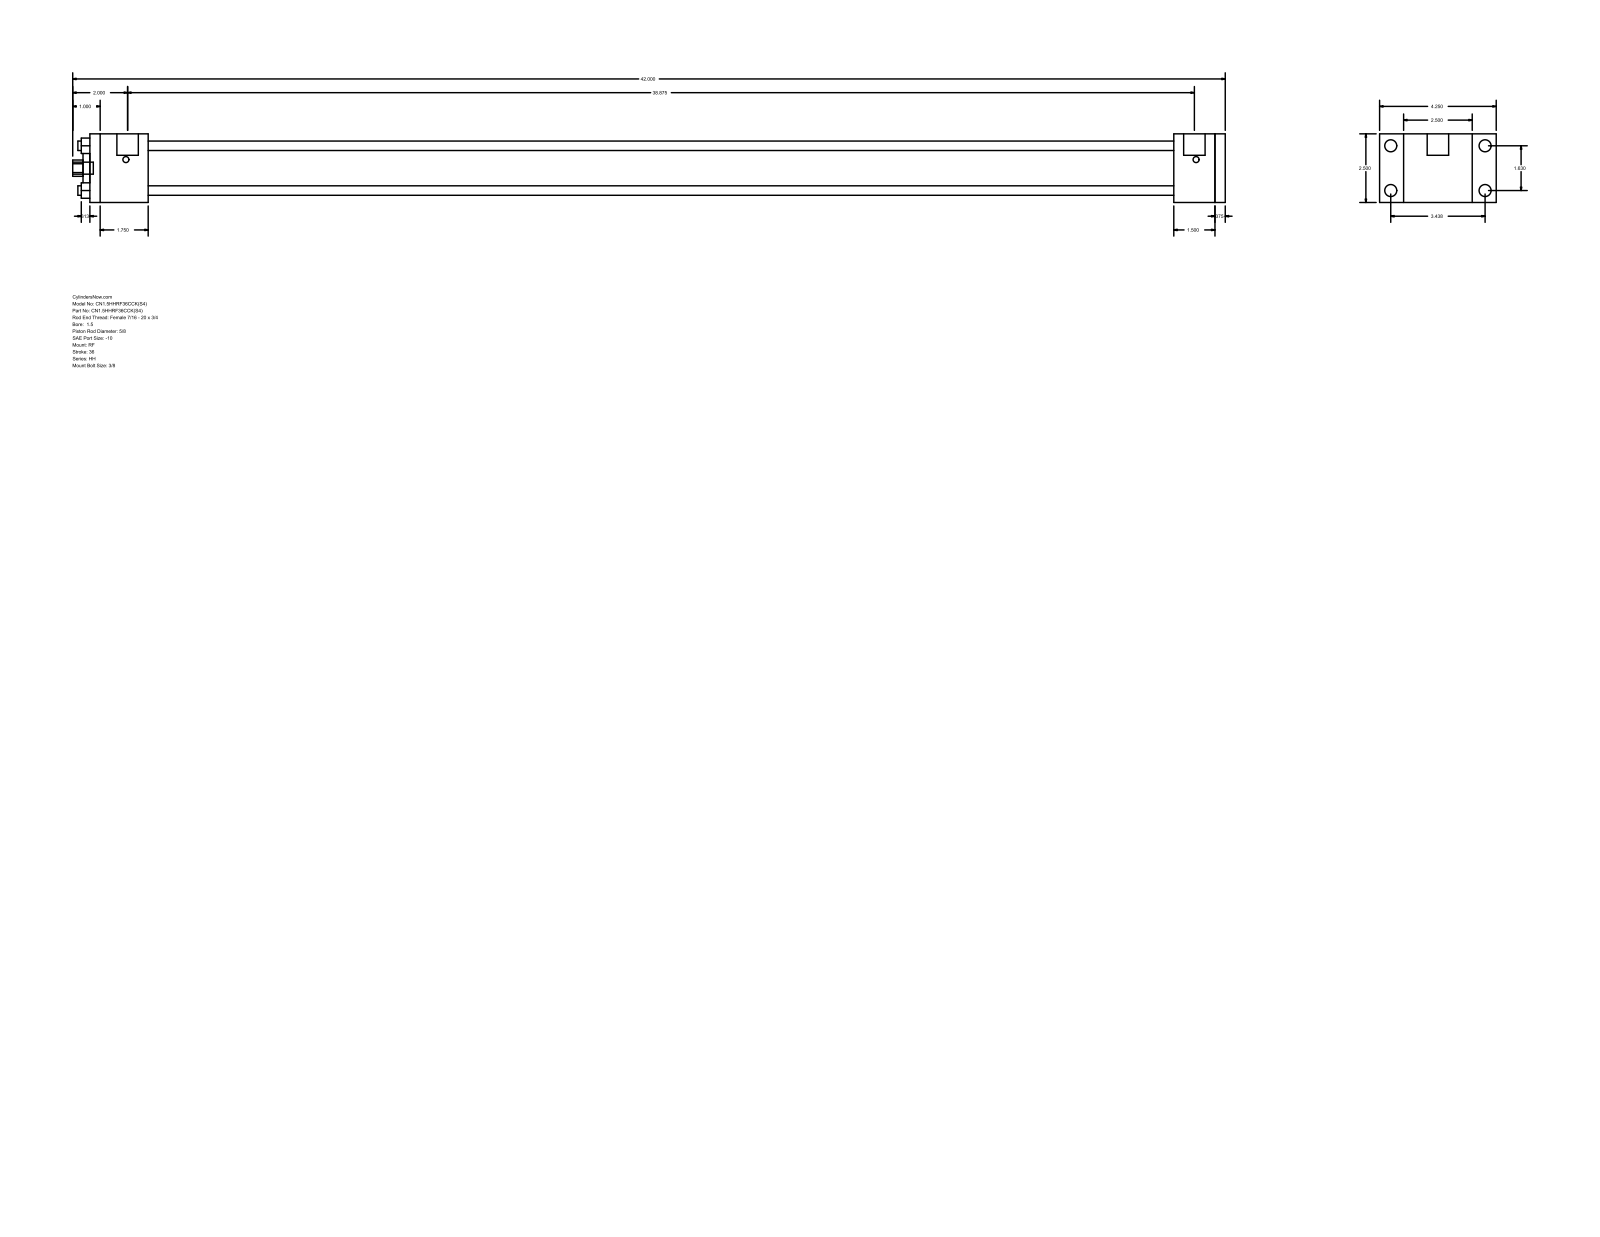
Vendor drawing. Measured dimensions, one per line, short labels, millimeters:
name: HH_RF__0150_0.625
written by: GSSL Pune (CONFIG_CONTROL_DESIGN)
unit: mm
bodies: 0 solids, 92 faces (64 planar, 28 cylindrical, 0 other)
size: 1066.8 × 107.95 × 63.5
holes: 4× ⌀8.76, 1× ⌀15.88, 1× ⌀28.57, 1× ⌀44.45
bosses: 4× ⌀11.13, 4× ⌀5.56, 2× ⌀19.84, 1× ⌀11.11
rounds: 1× R7.54
face distances: 63.5, 1050.92, 9.52, 1041.4, 47.63, 53.97, 1003.29, 949.32, 987.43, 996.95
hole spacings: 29.27, 41.4, 58.55
